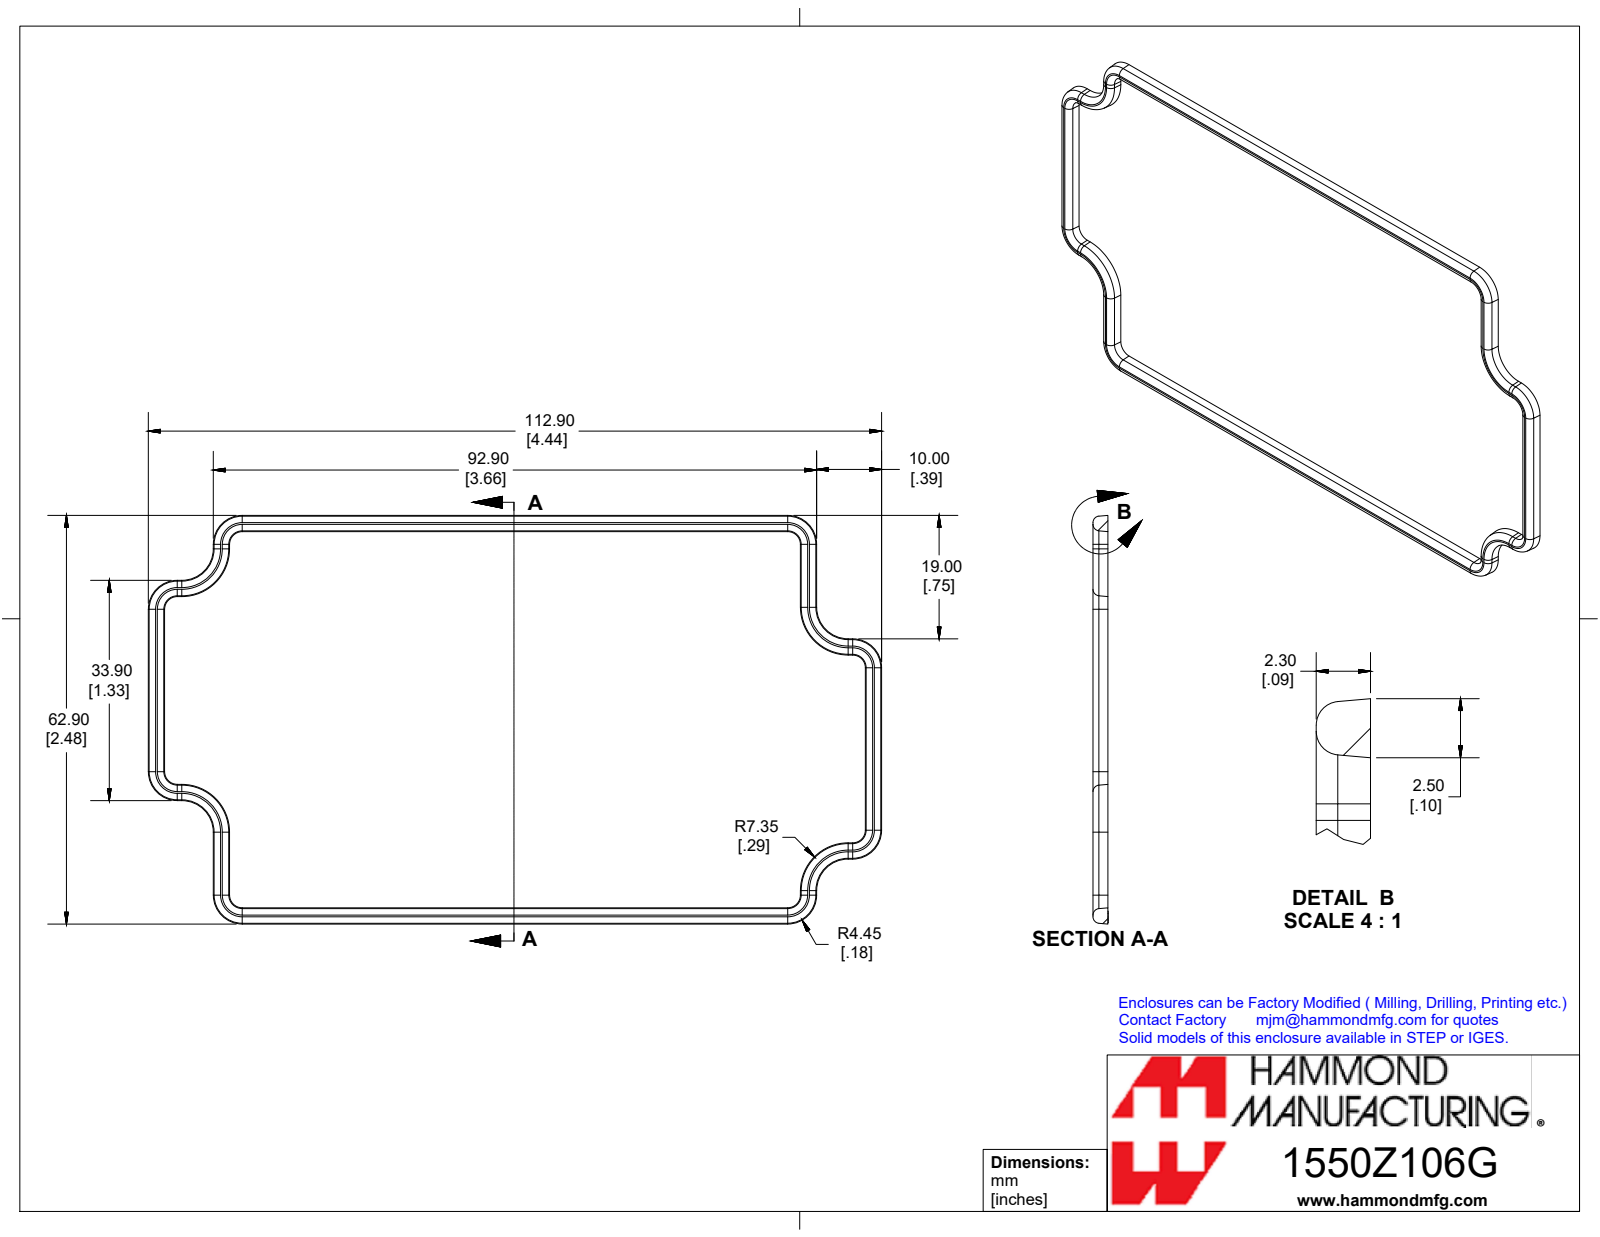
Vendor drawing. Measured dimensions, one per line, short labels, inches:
name: 1550Z106GASKET
written by: SolidWorks 2019 (CONFIG_CONTROL_DESIGN)
unit: in
bodies: 1 solid, 154 faces (40 planar, 24 cylindrical, 90 other)
size: 4.445 × 2.476 × 0.093
volume: 0.096 in³; area: 4.229 in²
rounds: 20× R0.039
face distances: 2.368, 0.091, 4.329, 0.392, 3.937, 3.544, 0.093, 0.745, 1.623, 1.976
